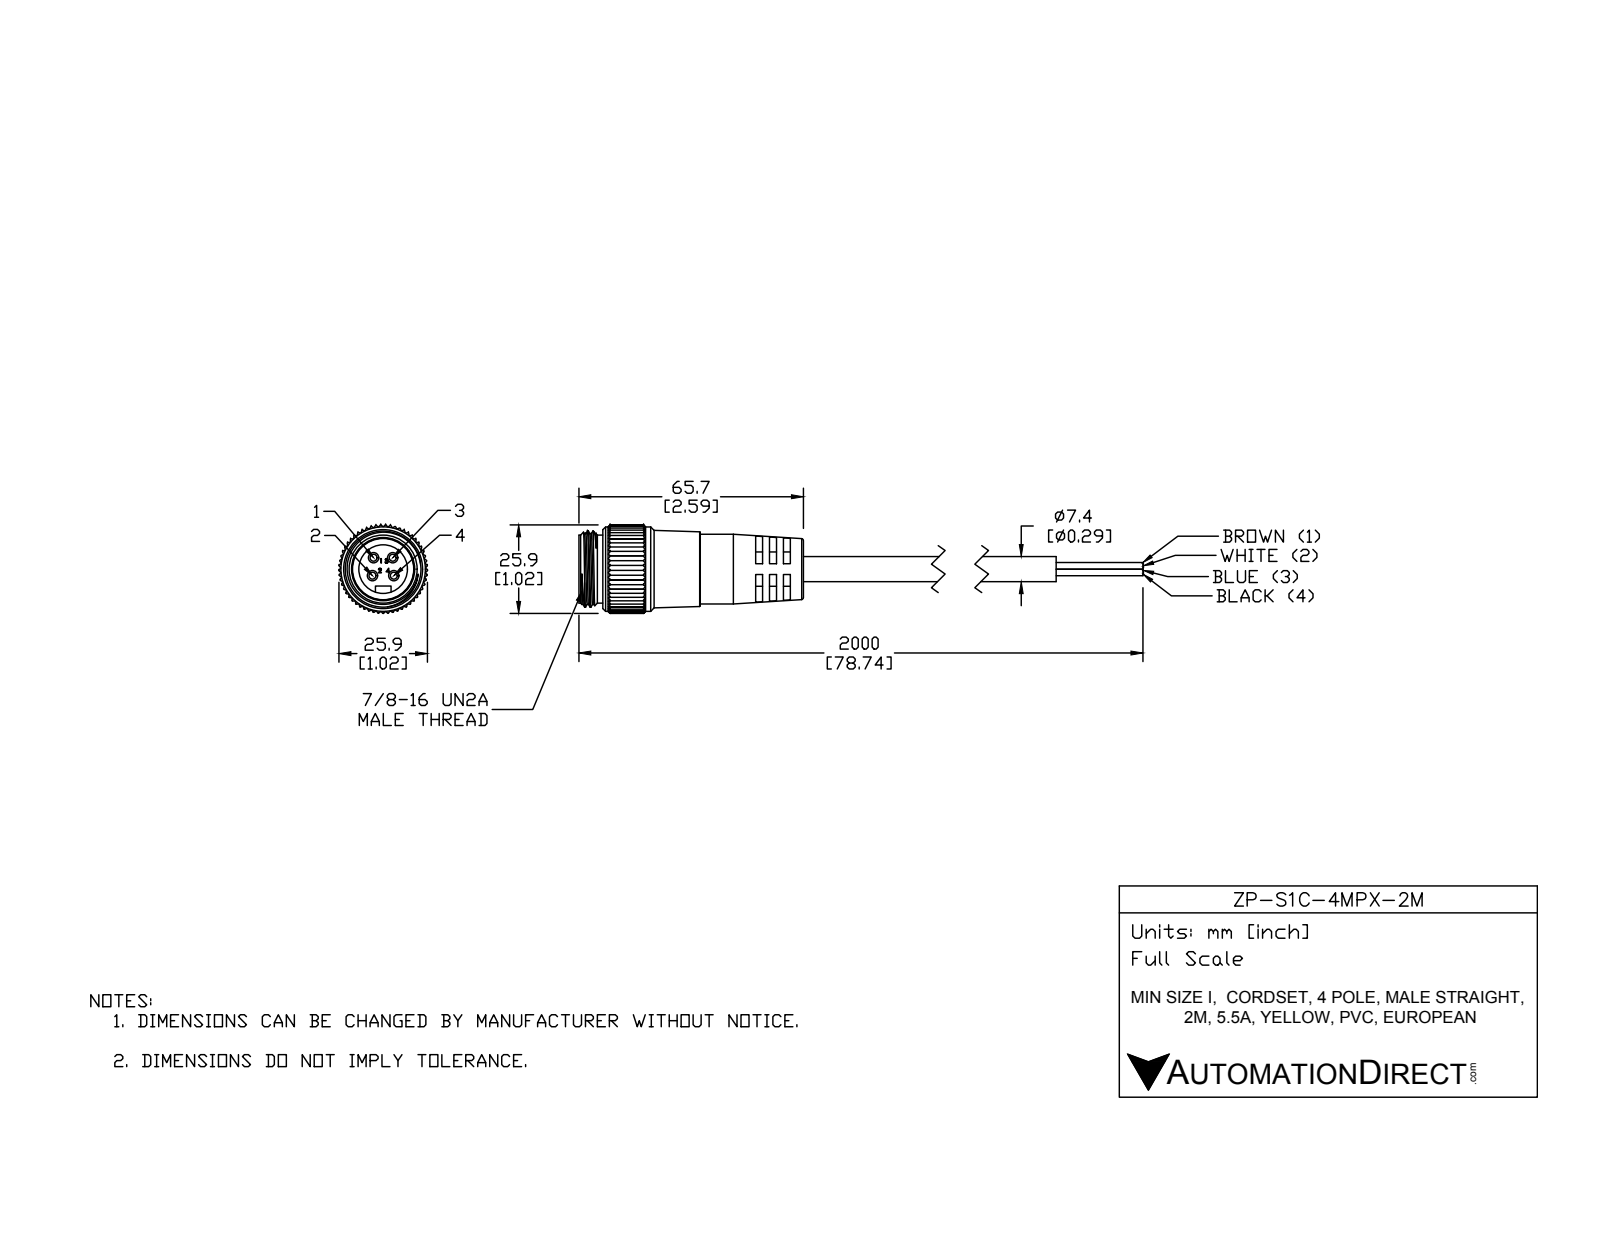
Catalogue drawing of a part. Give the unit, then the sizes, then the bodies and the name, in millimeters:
Units: millimetres
Overall size (bounding box): 115.9 × 25.84 × 25.83
Round holes (diameter × count): ⌀14.22 ×1, ⌀17.88 ×1, ⌀19.96 ×1, ⌀20.45 ×1, ⌀21 ×1
Round bosses / shafts (diameter × count): ⌀3.05 ×4, ⌀2 ×4, ⌀24.68 ×1, ⌀22.22 ×1, ⌀20.4 ×1, ⌀19.5 ×1, ⌀9.91 ×1
Partial cylindrical surfaces — rounded edges, fillets, slot ends (radius × count): R0.25 ×165, R2.29 ×1, R5.25 ×1, R12.93 ×1
Main face-to-face distances: 2, 4.04, 13.88, 11.88, 2.04, 9.84, 6.04, 7.84, 2.02, 8.06
Volume: 26 095 mm³ · Surface area: 13 335 mm²
Bodies: 6 solids, 606 faces (218 planar, 326 cylindrical, 62 other)
Part name (STEP PRODUCT): ZP-S1C-4MPX-2M
STEP written by: SolidWorks 2015 (AUTOMOTIVE_DESIGN)
